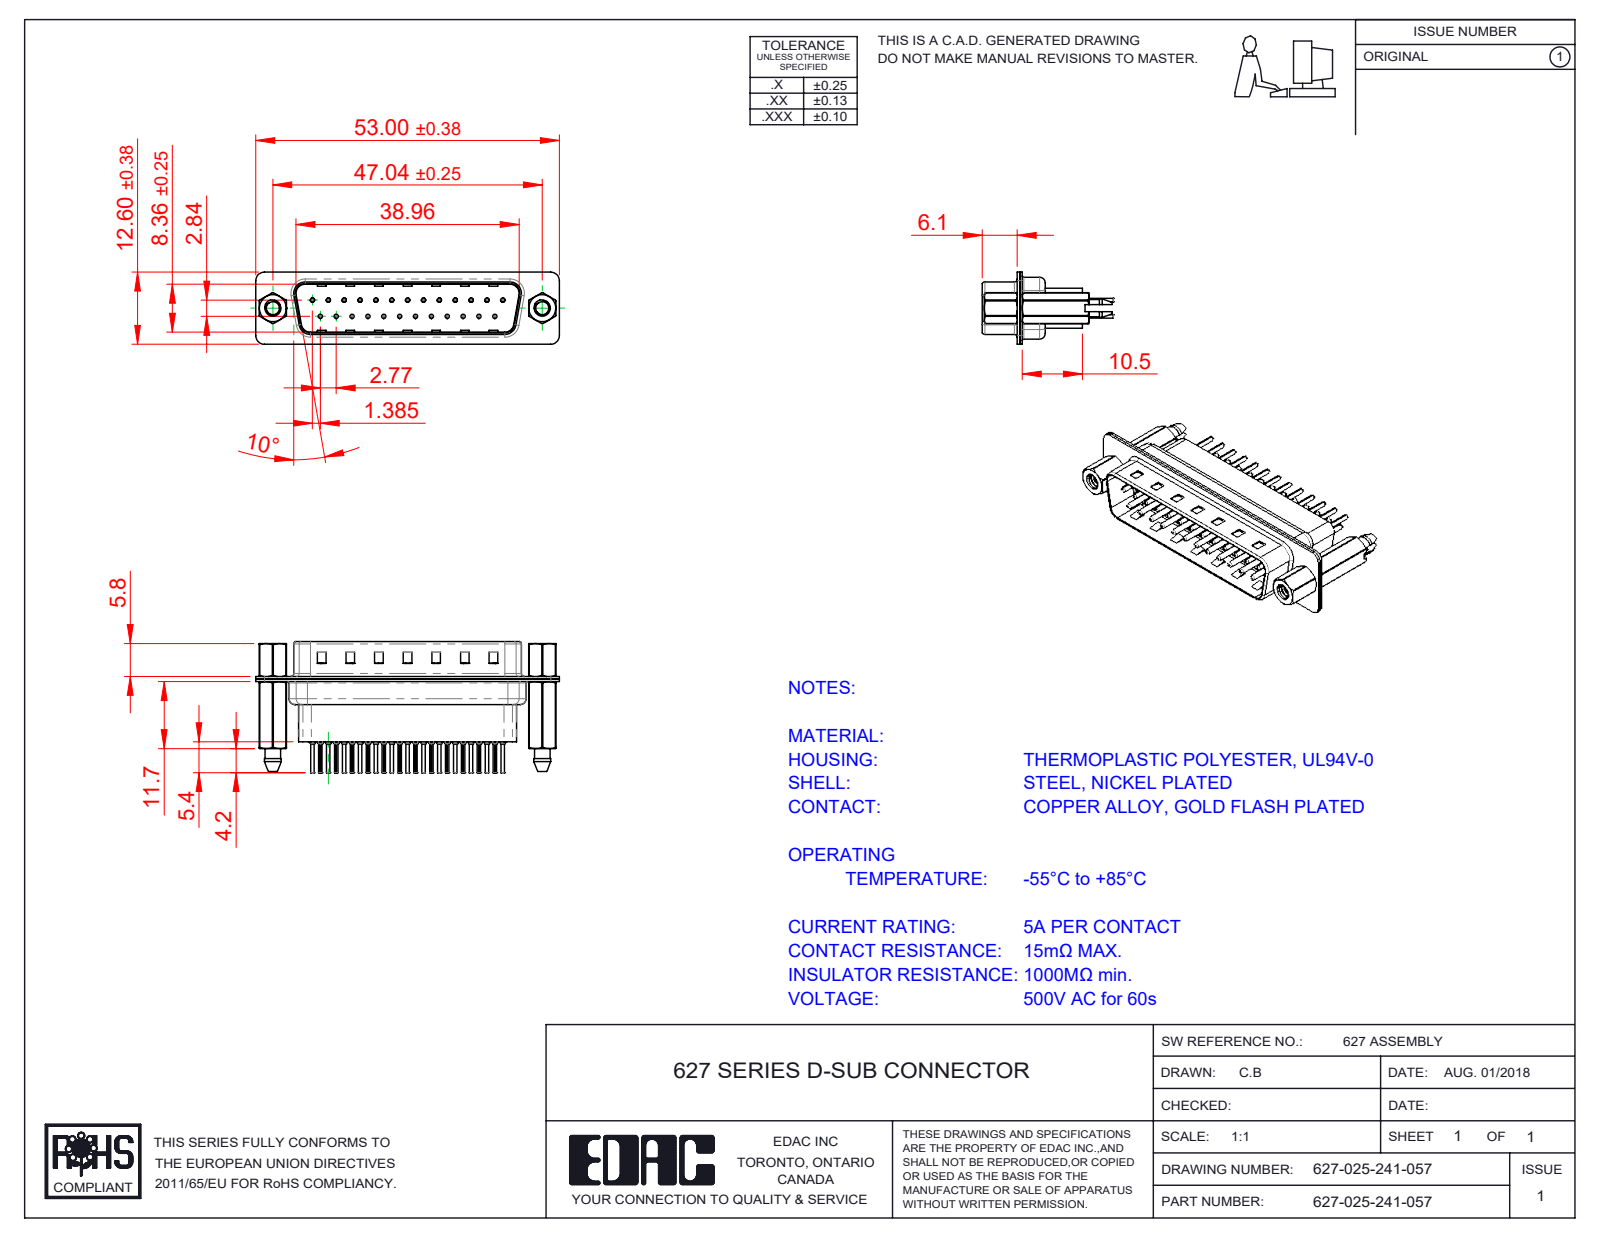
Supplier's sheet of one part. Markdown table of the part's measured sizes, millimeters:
| quantity | value |
| --- | --- |
| part name | 627 Shell Rear_25 Contacts; 627 Shell Front_25 Contacts; 627 Housing_25 HP; 627 Contact Row 2_41 (+4 more) |
| STEP written by | SolidWorks 2020 (CONFIG_CONTROL_DESIGN) |
| units | millimeters |
| bodies | 32 solids, 3060 faces (825 planar, 1200 cylindrical, 1035 other) |
| overall size | 53 × 22.8 × 12.6 |
| volume | 4 303 mm³ |
| surface area | 11 029 mm² |
| round holes (diameter × count) | 0.2 × 25, 0.35 × 25, 1.1 × 25, 1.6 × 25, 2.26 × 2, 2.29 × 2, 4 × 2, 4.8 × 2 |
| round bosses / shafts (diameter × count) | 2 × 25, 1.5 × 25, 0.75 × 25, 0.6 × 25, 4.9 × 2, 2.79 × 2 |
| partial cylindrical surfaces (radius × count) | 0.1 × 50, 1.5 × 18, 2 × 12, 1.6 × 10, 0.5 × 8, 0.25 × 4, 0.6 × 4, 0.65 × 4 |
| main face-to-face distances | 0.4, 0.45, 0.82, 9.58, 0.68, 7.68, 1.5, 0.9, 1.08, 8.08 |
| hole center spacings | 3.16, 8.31, 2.77, 5.54, 11.08, 16.62, 5.03, 5.04 |
